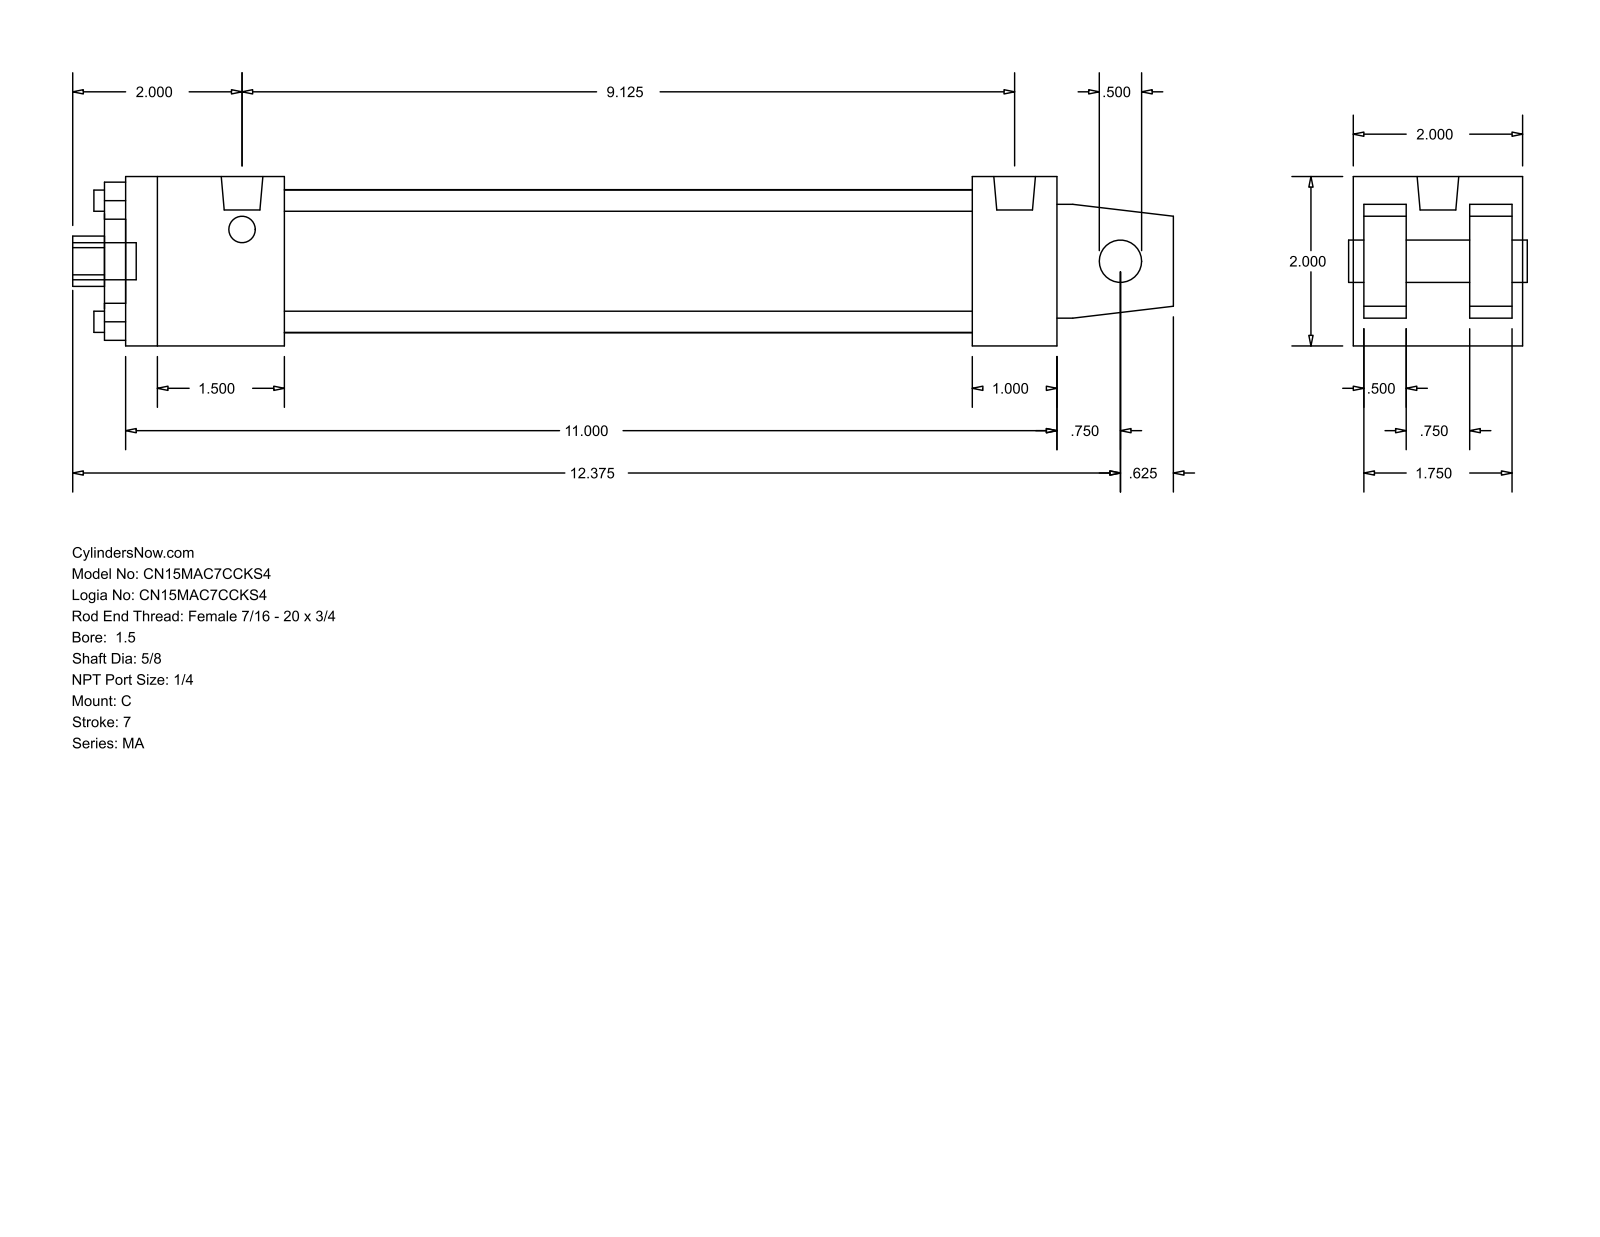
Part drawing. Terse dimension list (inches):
name: MA_C__0150_0.625
written by: GSSL Pune (CONFIG_CONTROL_DESIGN)
unit: in
bodies: 0 solids, 103 faces (76 planar, 27 cylindrical, 0 other)
size: 13 × 2 × 2
holes: 4× ⌀0.25, 1× ⌀0.5, 1× ⌀0.625, 1× ⌀1.125, 1× ⌀1.69
bosses: 4× ⌀0.313, 2× ⌀0.492, 1× ⌀0.437
rounds: 1× R0.297
face distances: 2, 1.375, 0.5, 0.125, 0.625, 1.875, 1.25, 11, 10, 1
hole spacings: 1.011, 1.43, 2.022
